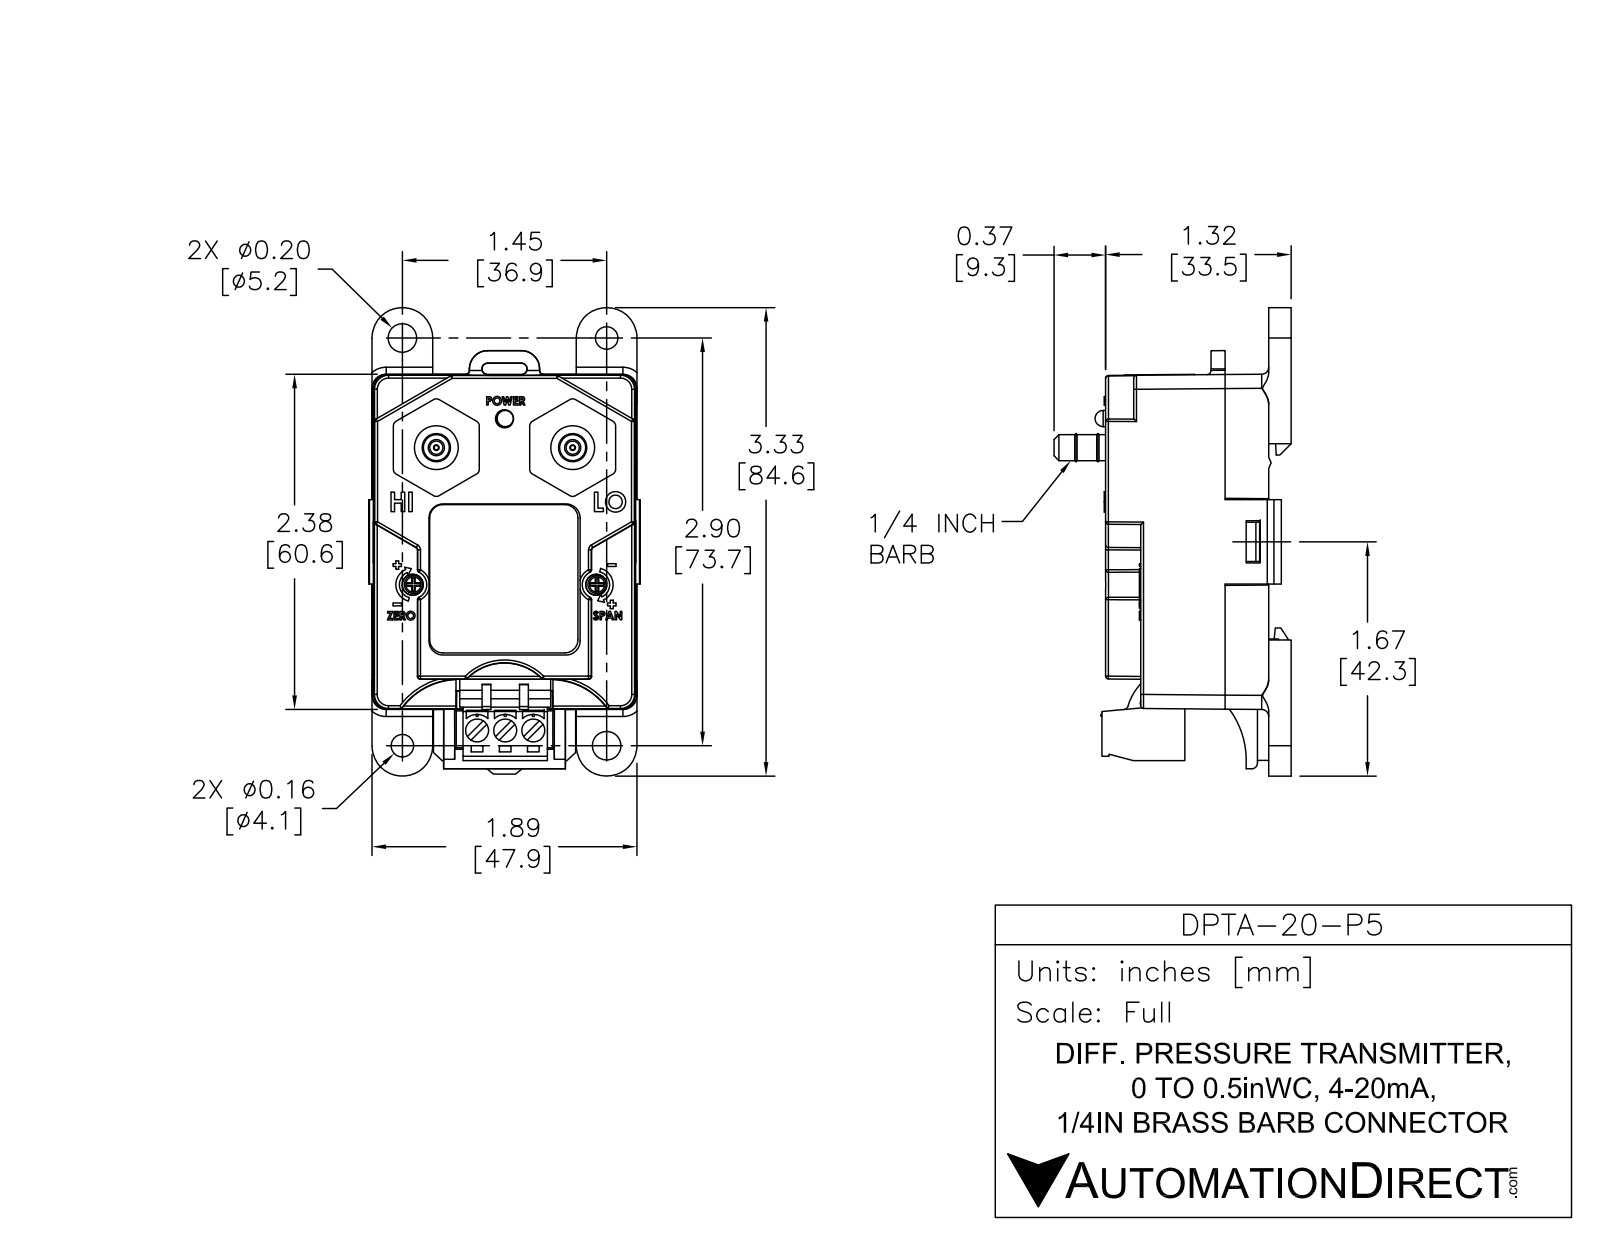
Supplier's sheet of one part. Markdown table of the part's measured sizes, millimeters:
| quantity | value |
| --- | --- |
| part name | DPTA-20-P5 |
| STEP written by | SolidWorks 2011 (AUTOMOTIVE_DESIGN) |
| units | millimeters |
| bodies | 11 solids, 448 faces (354 planar, 85 cylindrical, 9 other) |
| overall size | 85.01 × 49.76 × 43.1 |
| volume | 29 684 mm³ |
| surface area | 34 743 mm² |
| round holes (diameter × count) | 4 × 7, 2.5 × 2, 5.12 × 2, 3.1 × 1 |
| round bosses / shafts (diameter × count) | 5 × 3, 3.5 × 3, 3.5 × 3, 8 × 2, 4.75 × 2, 3 × 1 |
| partial cylindrical surfaces (radius × count) | 3 × 12, 2 × 4, 5.5 × 4, 0.99 × 2, 1.06 × 2, 1.12 × 2, 2.38 × 2, 3.25 × 2 |
| main face-to-face distances | 1, 1.9, 4, 29.1, 0.5, 46.9, 5.9, 5, 33.1, 27.2 |
| hole center spacings | 13.55, 20.73, 23.37, 24.92, 29.43, 34.46, 36.67, 38.22 |
